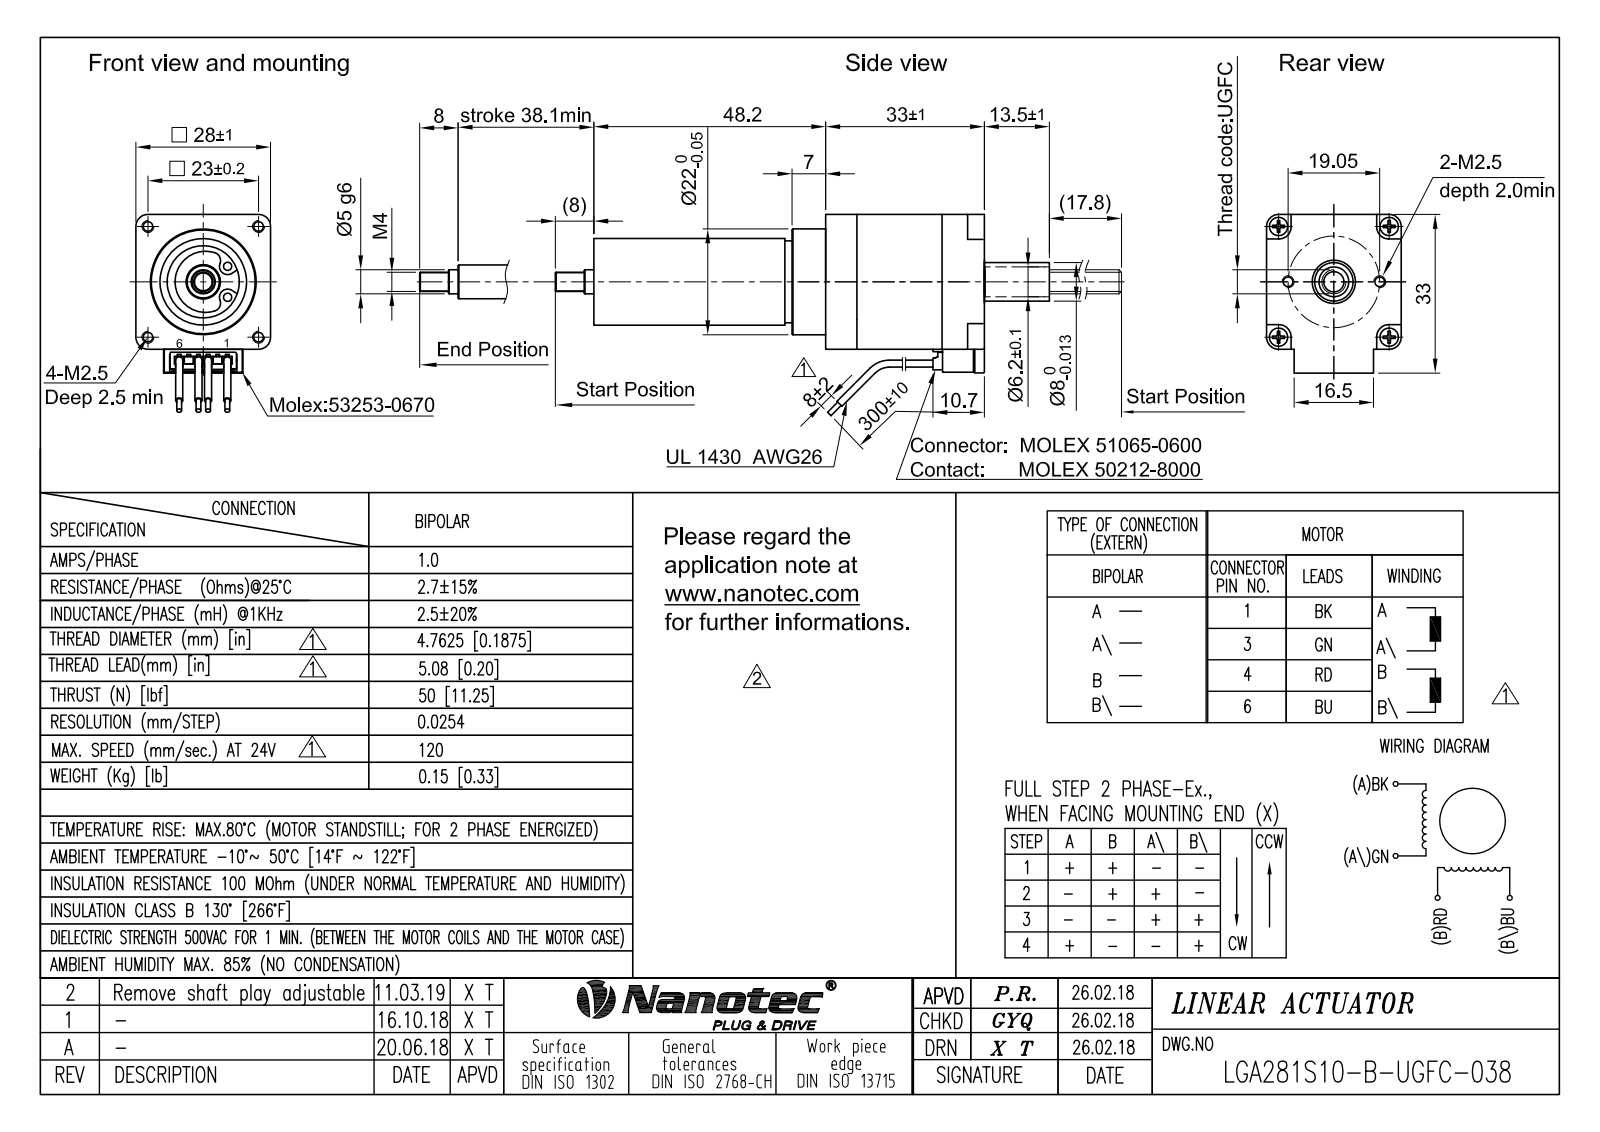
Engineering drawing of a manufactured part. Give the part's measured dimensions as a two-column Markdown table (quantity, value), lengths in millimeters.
| quantity | value |
| --- | --- |
| part name | 零件26 |
| STEP written by | Autodesk Inventor 2013 (CONFIG_CONTROL_DESIGN) |
| units | millimeters |
| bodies | 2 solids, 480 faces (339 planar, 60 cylindrical, 81 other) |
| overall size | 141.1 × 33 × 28 |
| volume | 40 534 mm³ |
| surface area | 11 994 mm² |
| round holes (diameter × count) | 2.05 × 4, 1.7 × 2, 2.01 × 2, 6 × 1, 6.2 × 1, 9 × 1, 9.5 × 1, 15 × 1 |
| round bosses / shafts (diameter × count) | 22 × 1, 18 × 1, 17 × 1, 8 × 1, 7 × 1, 5 × 1, 4.7 × 1, 4 × 1 |
| partial cylindrical surfaces (radius × count) | 0.5 × 5, 2.5 × 4, 0.6 × 3, 1 × 2, 7.11 × 2, 8.27 × 2, 4.2 × 1, 19 × 1 |
| main face-to-face distances | 28, 33.3, 0.4, 7, 40.3, 0.5, 2, 4.8, 1, 3.75 |
| hole center spacings | 11.67, 16.26, 23, 4.83, 6.12, 10.67, 15.27, 15.38 |
